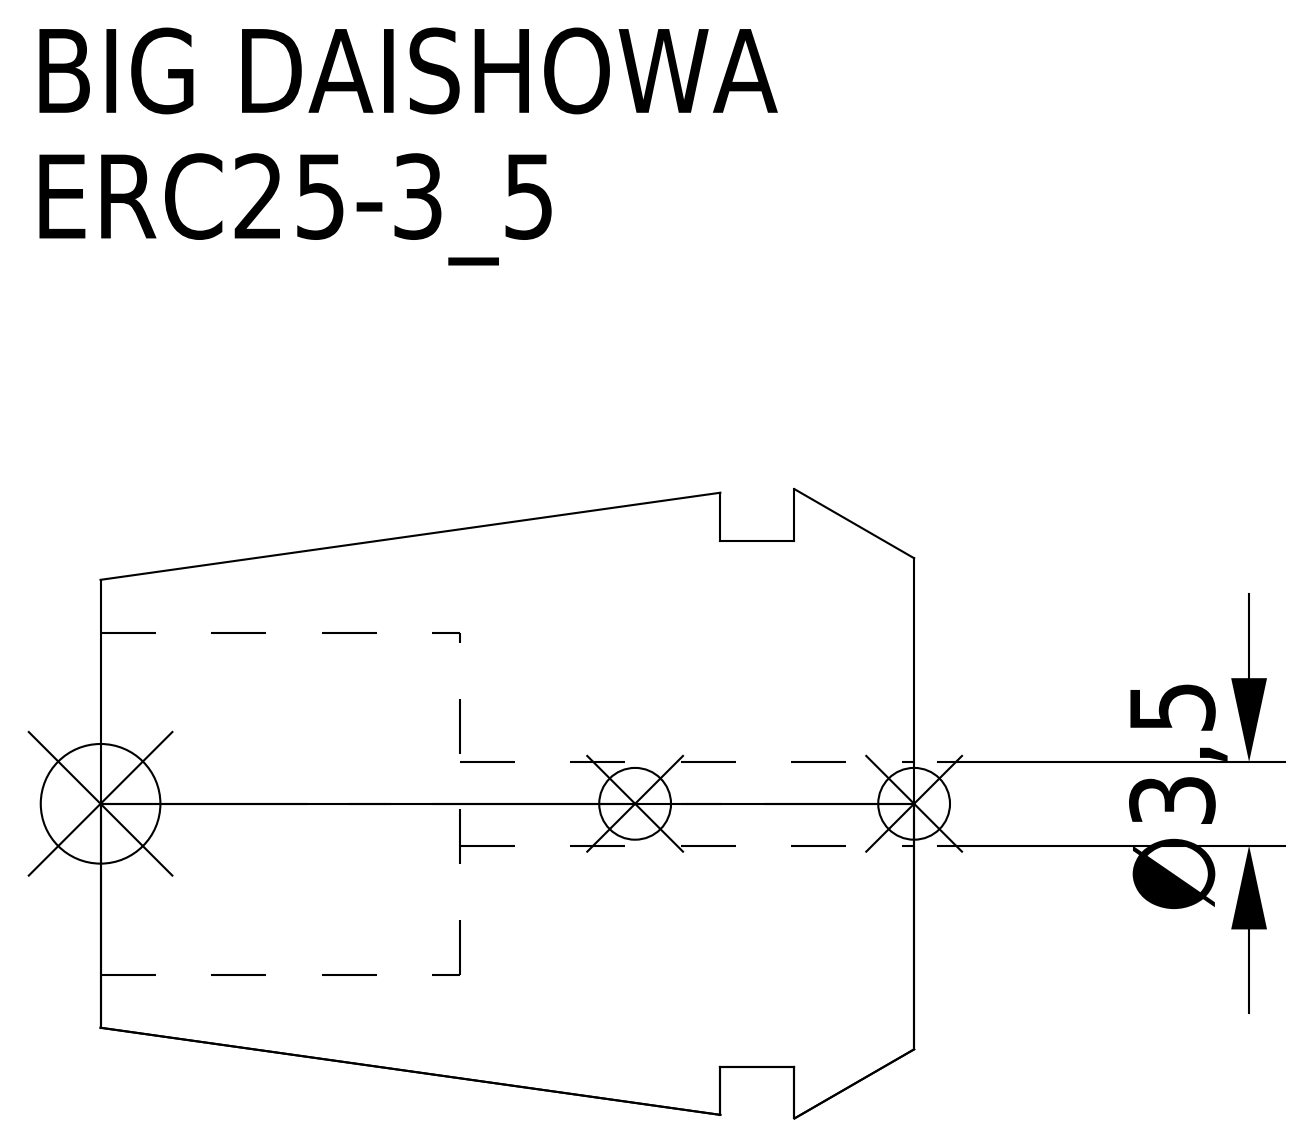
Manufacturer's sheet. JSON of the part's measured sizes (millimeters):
{"part_name": "ERC25-3_5", "step_written_by": "CREO PARAMETRIC BY PTC INC, 2016380 (AUTOMOTIVE_DESIGN)", "units": "millimeters", "bodies": {"solids": 1, "faces": 15, "planar": 5, "cylindrical": 6, "other": 4}, "overall_size": [34, 26.3, 26.3], "volume_mm3": 11011, "surface_area_mm2": 4260, "round_holes": [[3.5, 1], [14.3, 1]], "round_bosses_or_shafts": [[22, 1]], "face_to_face_distances": [5, 19, 14, 8.1, 3.1, 10.9, 34, 29, 25.9, 15]}
